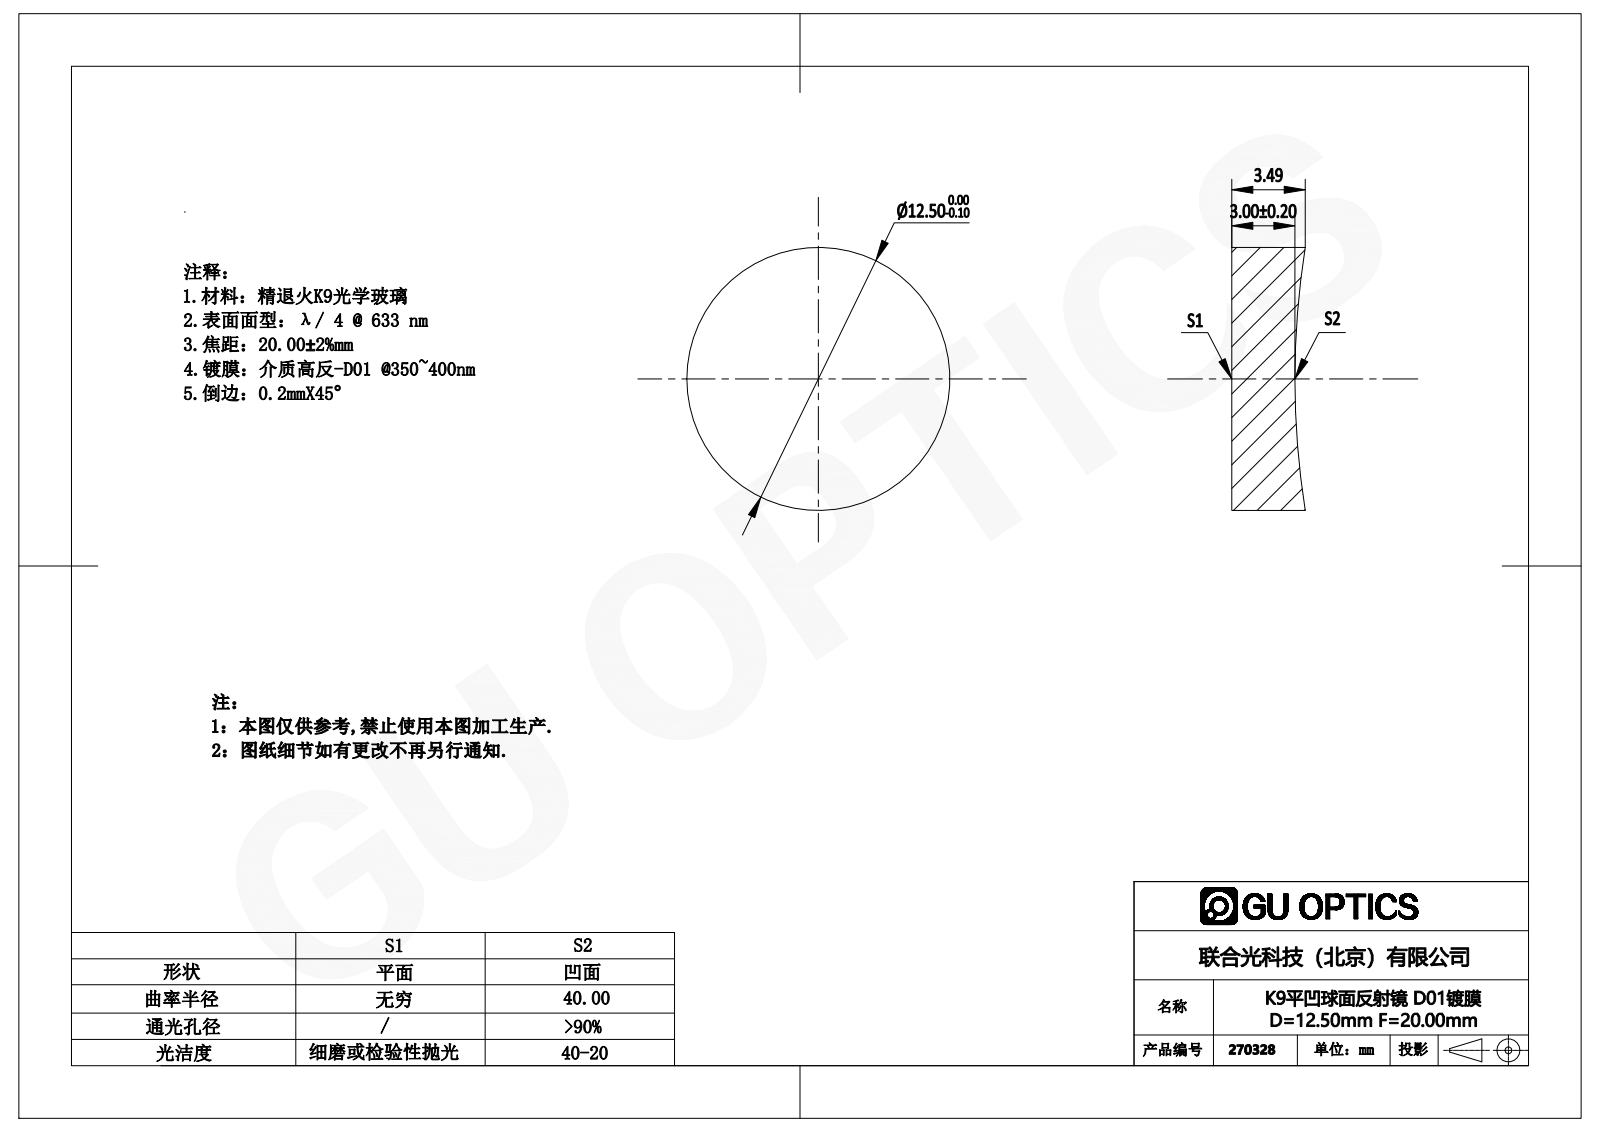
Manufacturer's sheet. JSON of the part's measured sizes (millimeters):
{"part_name": "270003", "step_written_by": "SolidWorks 2016 (AUTOMOTIVE_DESIGN)", "units": "millimeters", "bodies": {"solids": 1, "faces": 5, "planar": 1, "cylindrical": 2, "other": 2}, "overall_size": [12.5, 12.5, 3.49], "volume_mm3": 398, "surface_area_mm2": 383, "round_bosses_or_shafts": [[12.5, 1]]}
